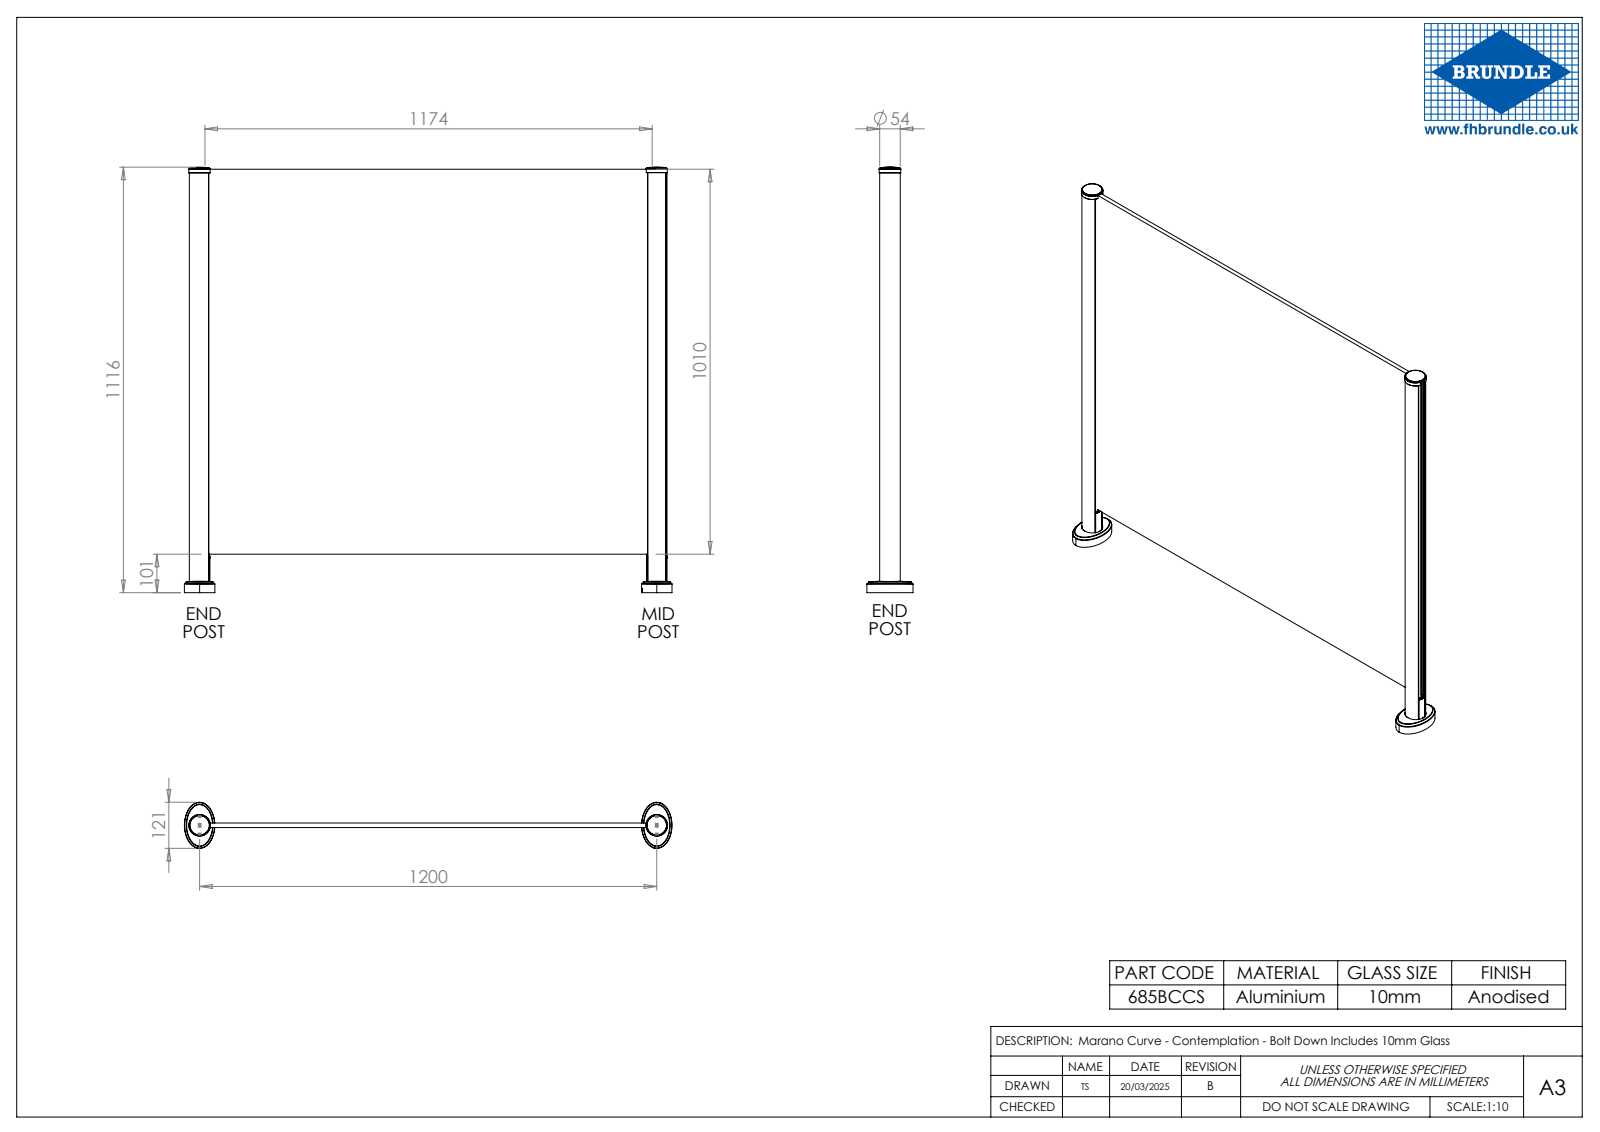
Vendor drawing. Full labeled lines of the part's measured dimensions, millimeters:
Part name (STEP PRODUCT): 68057 Part7; 68057 Part5_longer lenght; 6805791R54 Part2; 6805791R54_no top infill and no top packer (+8 more)
STEP written by: SolidWorks 2023 (CONFIG_CONTROL_DESIGN)
Units: millimetres
Bodies: 33 solids, 1554 faces (498 planar, 682 cylindrical, 374 other)
Overall size (bounding box): 1280 × 1117 × 121
Volume: 16 500 000 mm³ · Surface area: 3 924 000 mm²
Round holes (diameter × count): ⌀8 ×6, ⌀18 ×6, ⌀15 ×4, ⌀5 ×2, ⌀10 ×2, ⌀54.5 ×2
Round bosses / shafts (diameter × count): ⌀4.8 ×8, ⌀3.84 ×8, ⌀56.5 ×2, ⌀54 ×2
Partial cylindrical surfaces — rounded edges, fillets, slot ends (radius × count): R0.5 ×180, R1 ×51, R5 ×22, R2.5 ×16, R0.6 ×15, R3 ×15, R1.5 ×14, R0.8 ×12
Main face-to-face distances: 12, 18.33, 1216, 64.8, 3, 1213, 1210, 1207, 6, 61.67
Hole centre spacings: 1200, 20, 21.5, 41.5, 61.5, 1200.17, 1200.19, 1200.72
